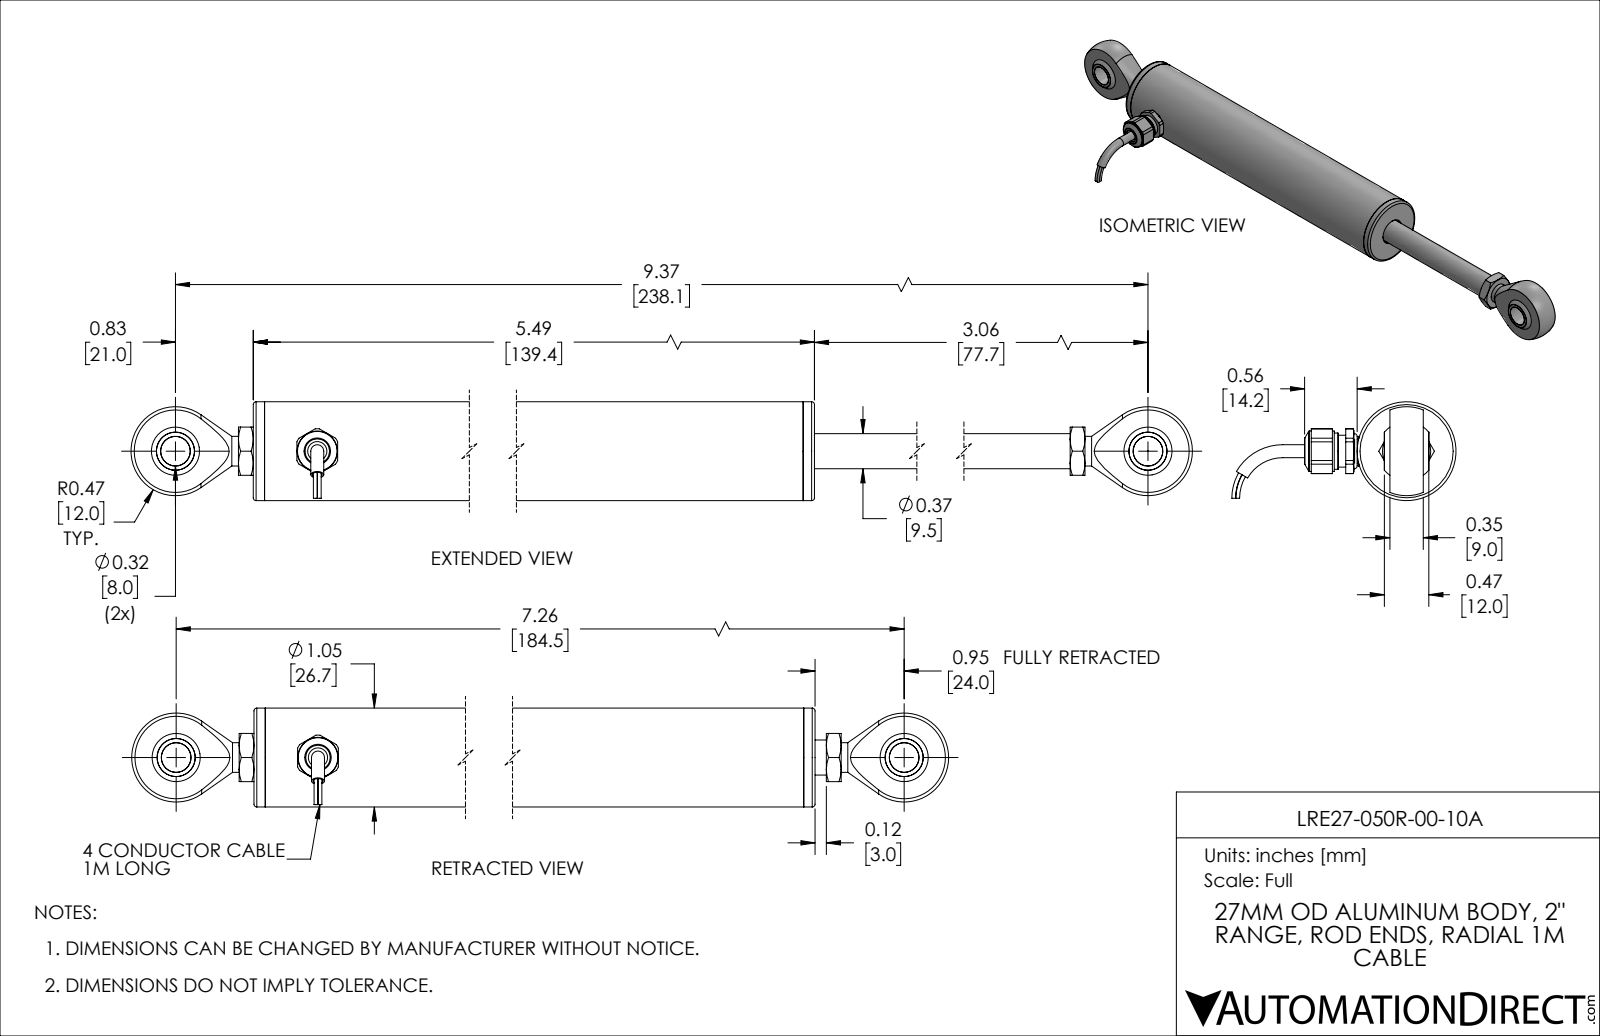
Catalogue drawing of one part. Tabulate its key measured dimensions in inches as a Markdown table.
| quantity | value |
| --- | --- |
| part name | LRE27-050R-00-10A |
| STEP written by | SolidWorks 2019 (AUTOMOTIVE_DESIGN) |
| units | inches |
| bodies | 17 solids, 225 faces (82 planar, 57 cylindrical, 86 other) |
| overall size | 8.208 × 2.382 × 1.05 |
| volume | 3.305 in³ |
| surface area | 66.07 in² |
| round holes (diameter × count) | 0.268 × 2, 0.315 × 2, 0.106 × 1, 0.138 × 1, 0.201 × 1, 0.205 × 1, 0.25 × 1, 0.274 × 1, 0.36 × 1, 0.375 × 1, 0.386 × 1, 0.499 × 1 |
| round bosses / shafts (diameter × count) | 0.039 × 4, 0.315 × 2, 1.05 × 1, 0.848 × 1, 0.5 × 1, 0.429 × 1, 0.386 × 1, 0.373 × 1 |
| partial cylindrical surfaces (radius × count) | 0.238 × 1 |
| main face-to-face distances | 0.12, 5.37, 0.354, 5.49, 5.25, 0.4, 0.28, 4.97, 5.09, 0.157 |
| hole center spacings | 1.507, 5.757, 7.264 |
